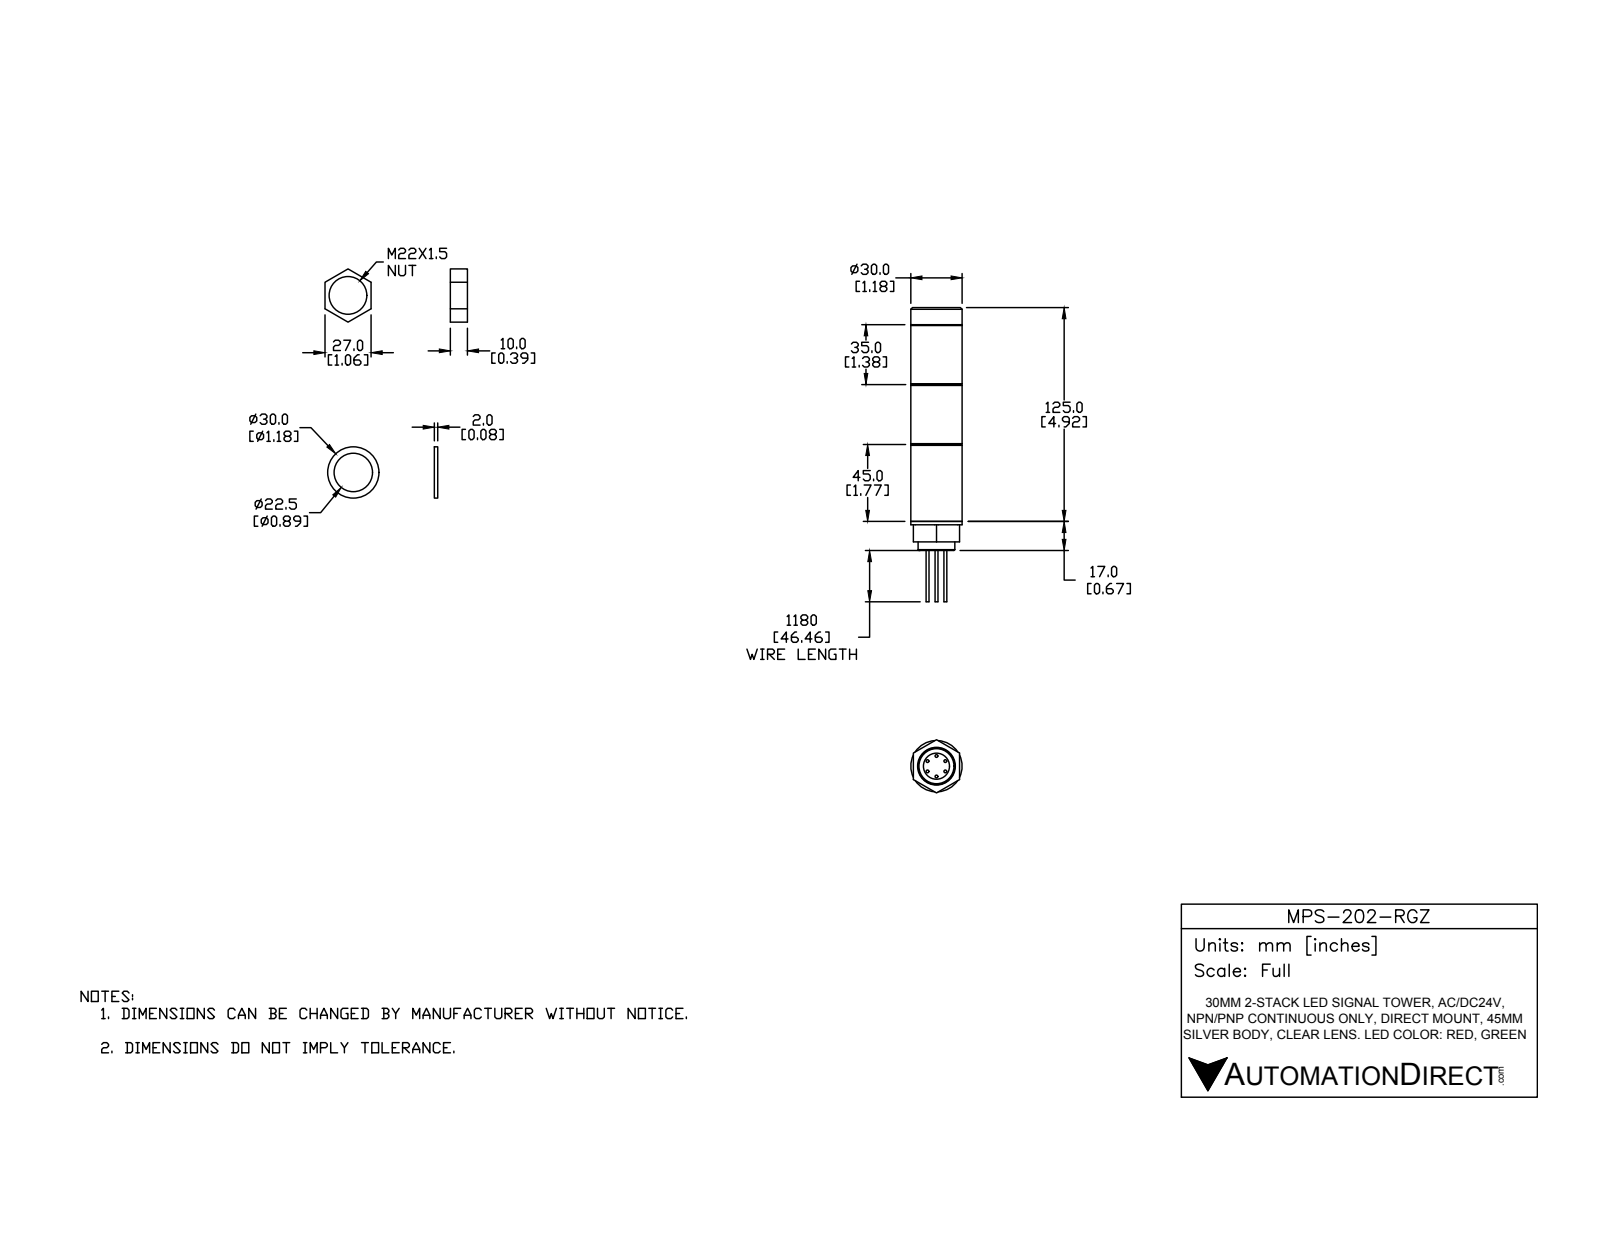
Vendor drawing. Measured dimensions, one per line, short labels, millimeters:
name: MPS-202-RGZ
written by: SolidWorks 2016 (AUTOMOTIVE_DESIGN)
unit: mm
bodies: 13 solids, 103 faces (49 planar, 38 cylindrical, 16 other)
size: 172 × 31.18 × 30
volume: 84 304 mm³; area: 27 566 mm²
holes: 1× ⌀3.2, 1× ⌀7.7, 1× ⌀15.3, 1× ⌀20.7, 1× ⌀22
bosses: 6× ⌀1.7, 1× ⌀30, 1× ⌀21.5, 1× ⌀5
face distances: 35, 45, 80, 70, 47, 82, 127, 115, 10, 92
